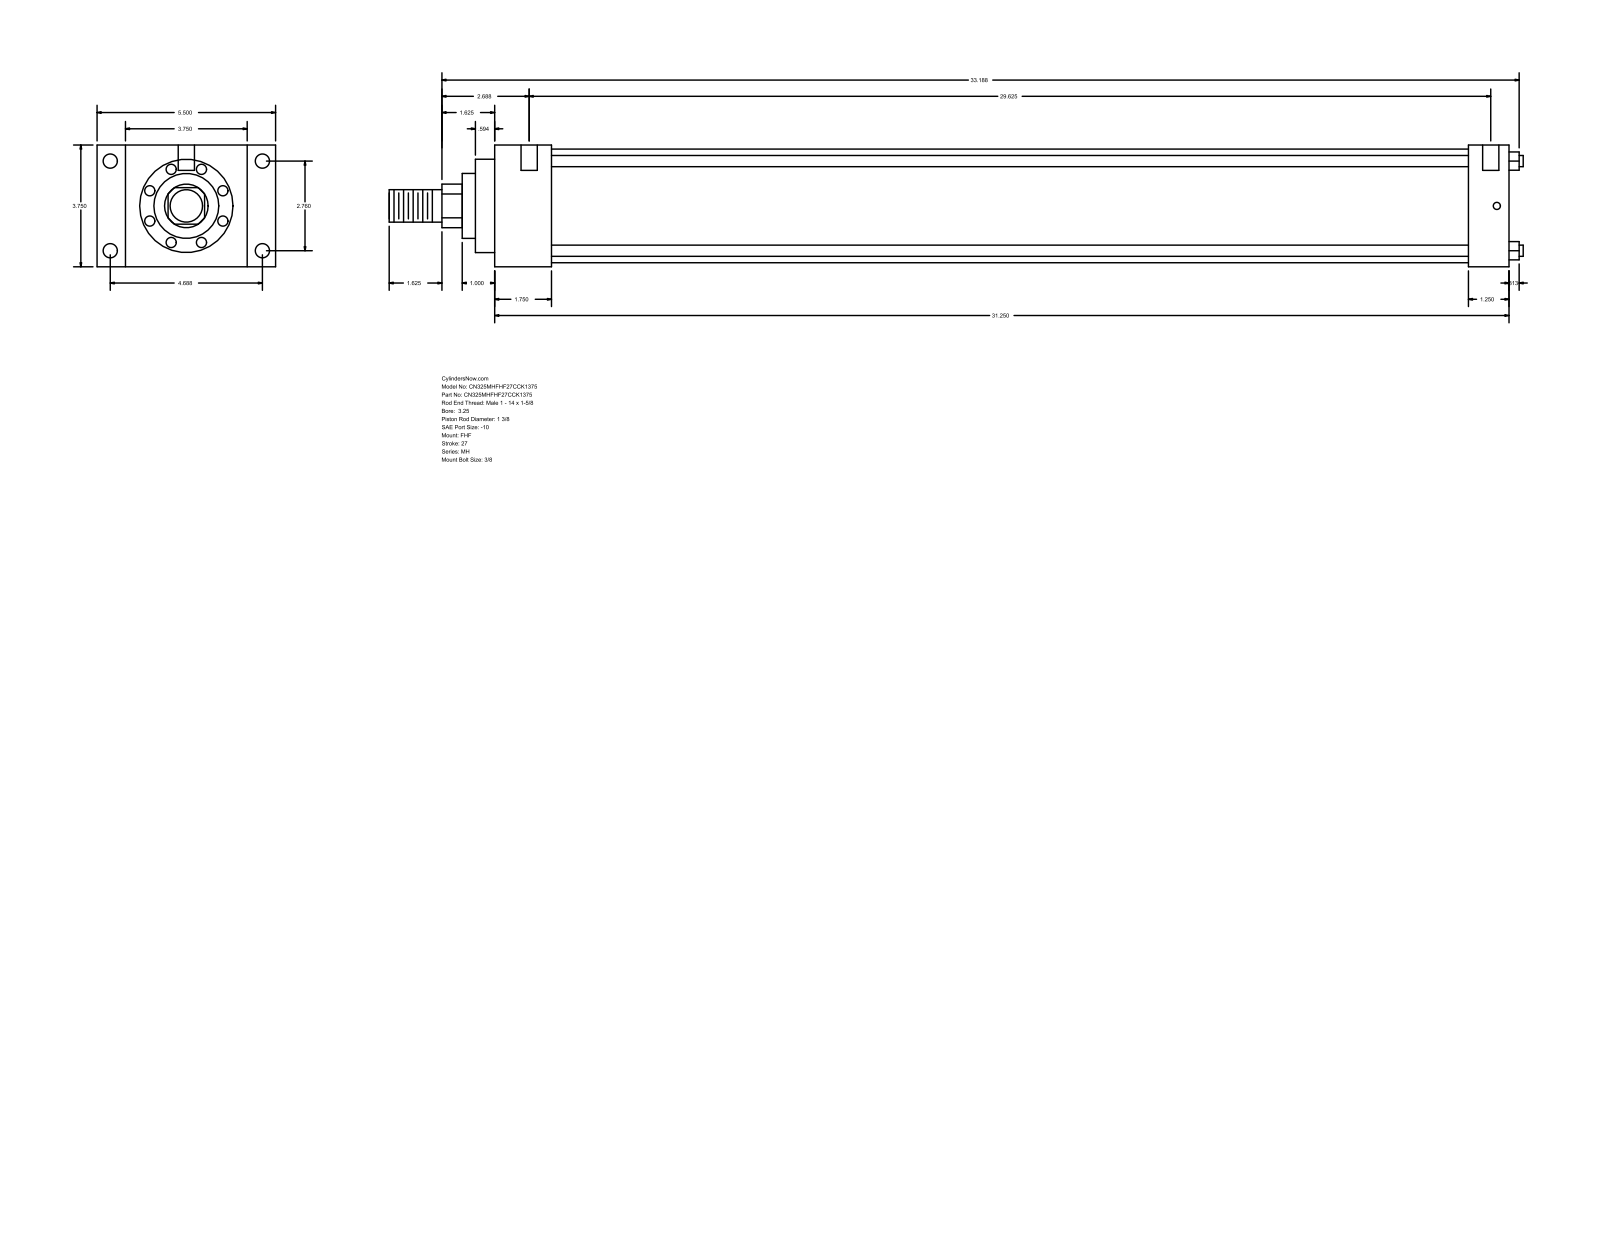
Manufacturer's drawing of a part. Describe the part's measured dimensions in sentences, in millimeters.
The part is named "MH_FHF__0325_1.375". Its 3-D file was written by "GSSL Pune (CONFIG_CONTROL_DESIGN)". It is 0 solids with 90 faces: 61 planar, 29 cylindrical and 0 other. Overall it measures 887.41 by 139.7 by 95.25 millimeters. Round holes: 4 of diameter 5.56, 4 of diameter 11.13, 2 of diameter 12.7. Round bosses or shafts: 4 of diameter 8.76, 1 of diameter 88.9, 1 of diameter 73.03, 1 of diameter 50.8, 1 of diameter 34.92, 1 of diameter 25.4. Partial cylindrical surfaces (rounded edges, fillets, slot ends): 1 of radius 17.06. The main face-to-face distances are 95.24, 793.75, 44.45, 749.3, 22.23, 117.47, 139.7, 762, 717.55, 31.75. The hole center spacings are 70.1, 119.06, 138.16, 758.83, 1.59, 4.76, 752.48, 754.07.
